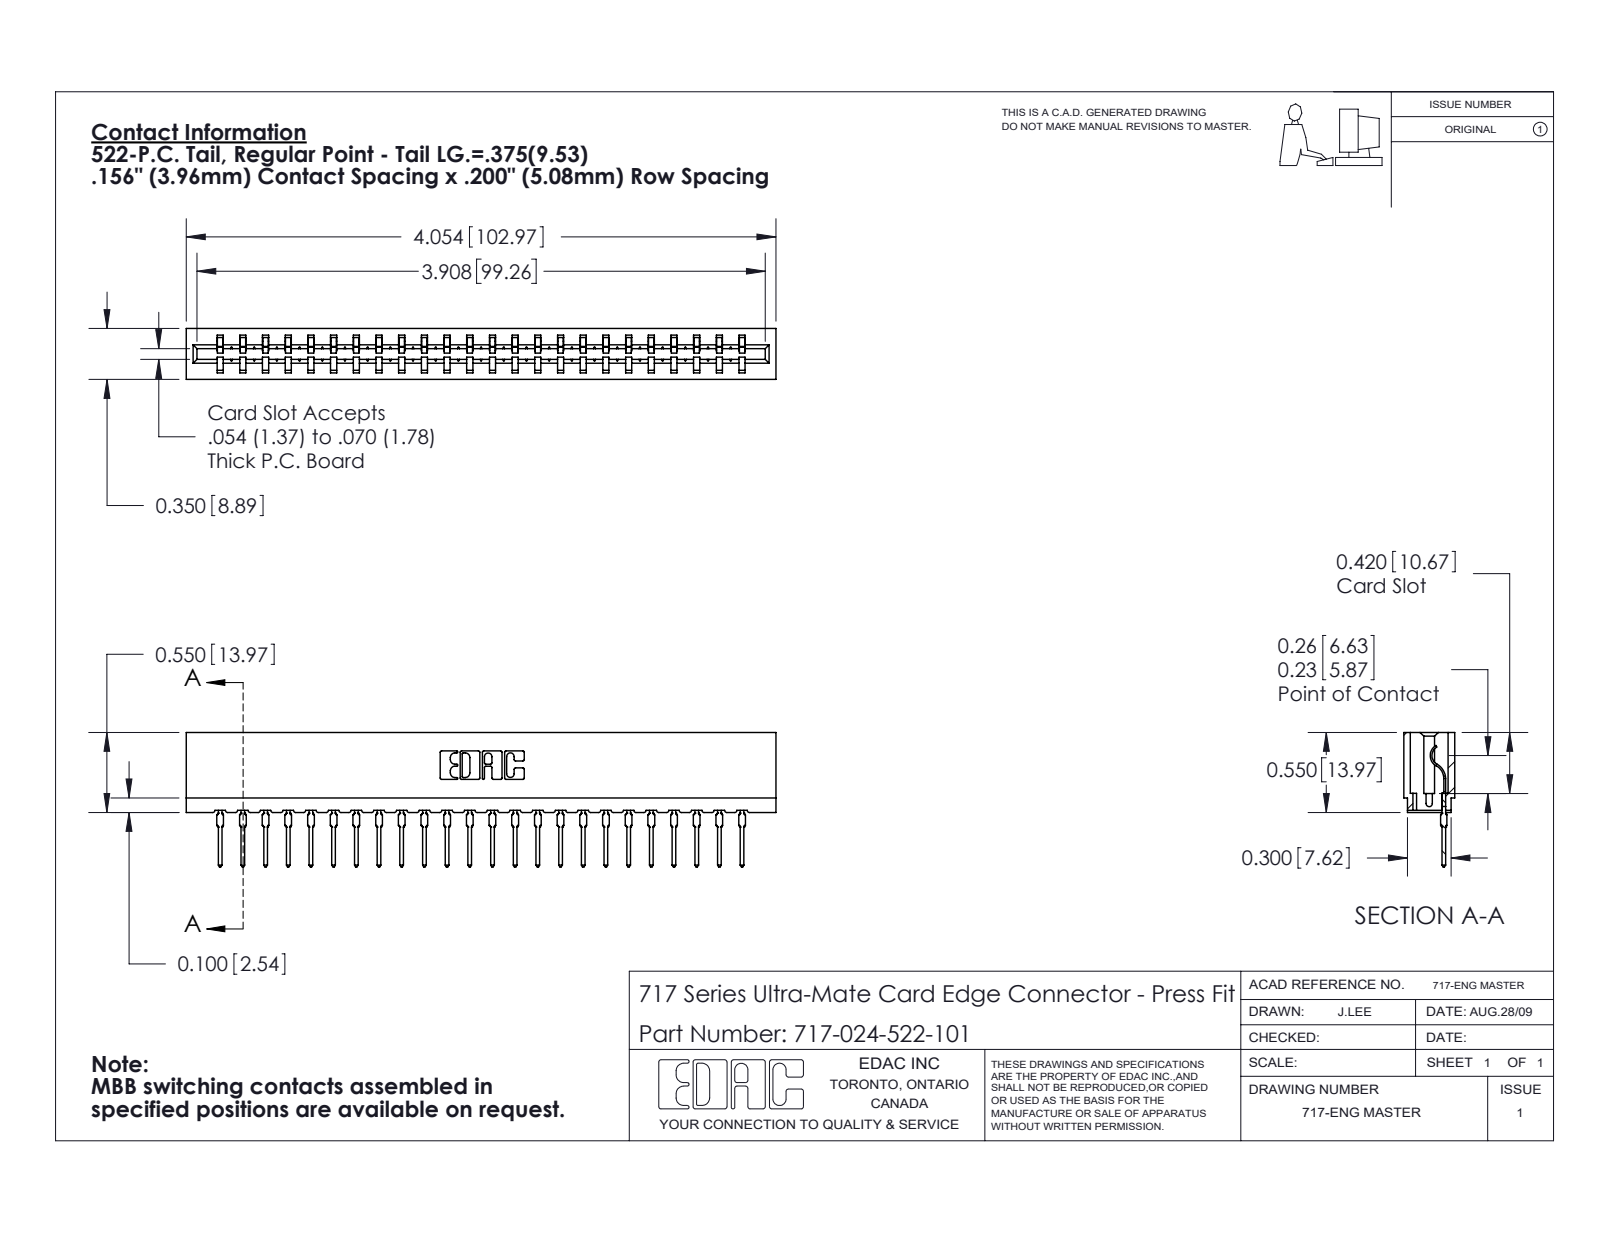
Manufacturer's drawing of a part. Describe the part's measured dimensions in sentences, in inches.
The part is named "717 Part_Insulator Option - 06; 717-024-522-101; 745-292-001_522". Its 3-D file was written by "SolidWorks 2020 (CONFIG_CONTROL_DESIGN)". It is 25 solids with 2806 faces: 1686 planar, 496 cylindrical and 624 other. Overall it measures 4.054 by 0.924 by 0.35 inches. Its volume is 0.536 cubic inches and its surface area 18.91 square inches. Partial cylindrical surfaces (rounded edges, fillets, slot ends): 48 of radius 0.015, 48 of radius 0.021, 22 of radius 0.01, 6 of radius 0.007, 6 of radius 0.031, 4 of radius 0.005, 4 of radius 0.011, 3 of radius 0.026. The main face-to-face distances are 0.212, 0.138, 0.35, 0.156, 0.074, 0.624, 0.468, 0.045, 0.305, 0.093.
